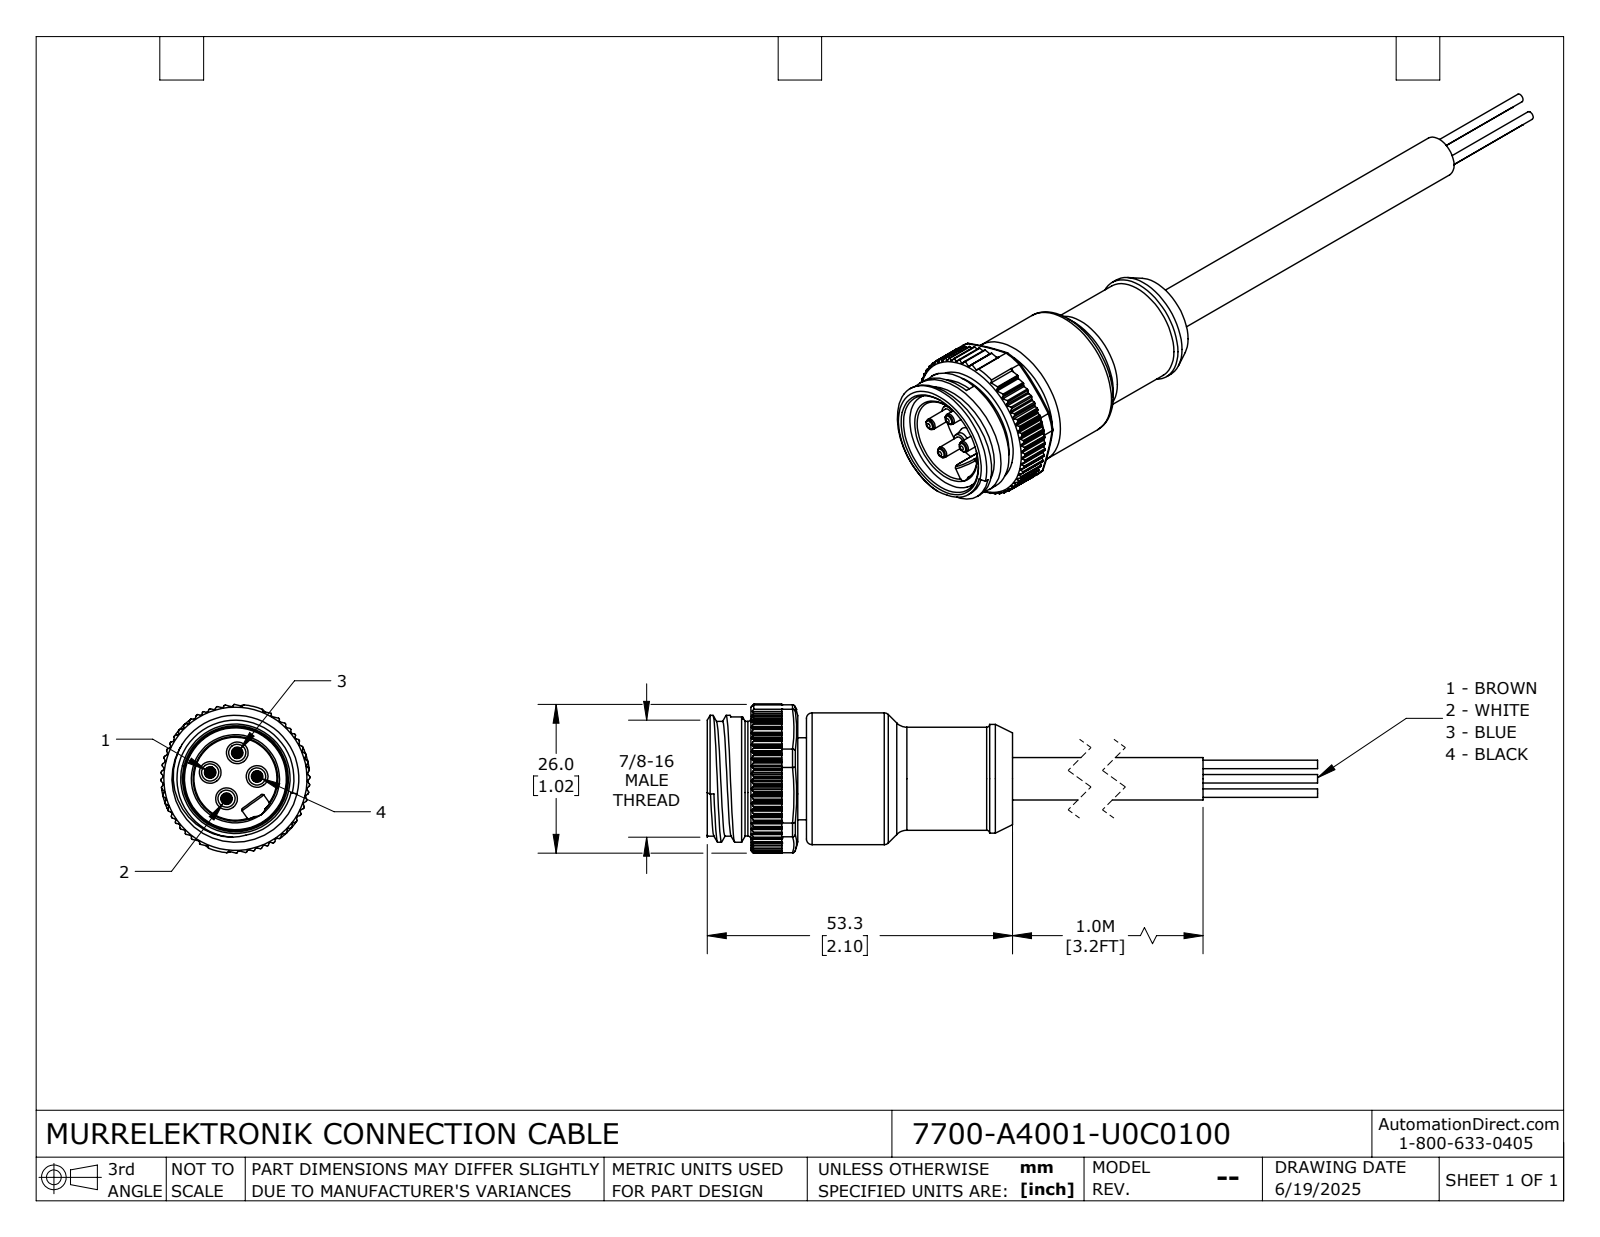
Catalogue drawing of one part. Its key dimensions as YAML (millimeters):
part_name: "7700-A4001-U0C0100"
step_written_by: "SolidWorks 2024 (CONFIG_CONTROL_DESIGN)"
units: millimeters
bodies: {solids: 1, faces: 580, planar: 236, cylindrical: 266, other: 78}
overall_size: [143.3, 26, 26]
volume: 20106
surface_area: 9287
round_holes:
  - {diameter: 15.6, count: 1}
  - {diameter: 18.5, count: 1}
round_bosses_or_shafts:
  - {diameter: 3, count: 4}
  - {diameter: 2, count: 4}
  - {diameter: 1.5, count: 4}
  - {diameter: 23, count: 1}
  - {diameter: 22.17, count: 1}
  - {diameter: 20.05, count: 1}
  - {diameter: 20, count: 1}
  - {diameter: 19, count: 1}
partial_cylinders:
  - {radius: 0.2, count: 126}
  - {radius: 0.3, count: 18}
  - {radius: 0.1, count: 4}
  - {radius: 0.7, count: 4}
  - {radius: 2.35, count: 1}
  - {radius: 13, count: 1}
face_to_face_distances: [1.5, 37.5, 36, 8.2, 9.7, 45.7, 0.9, 7.3, 8.8, 44.8]
